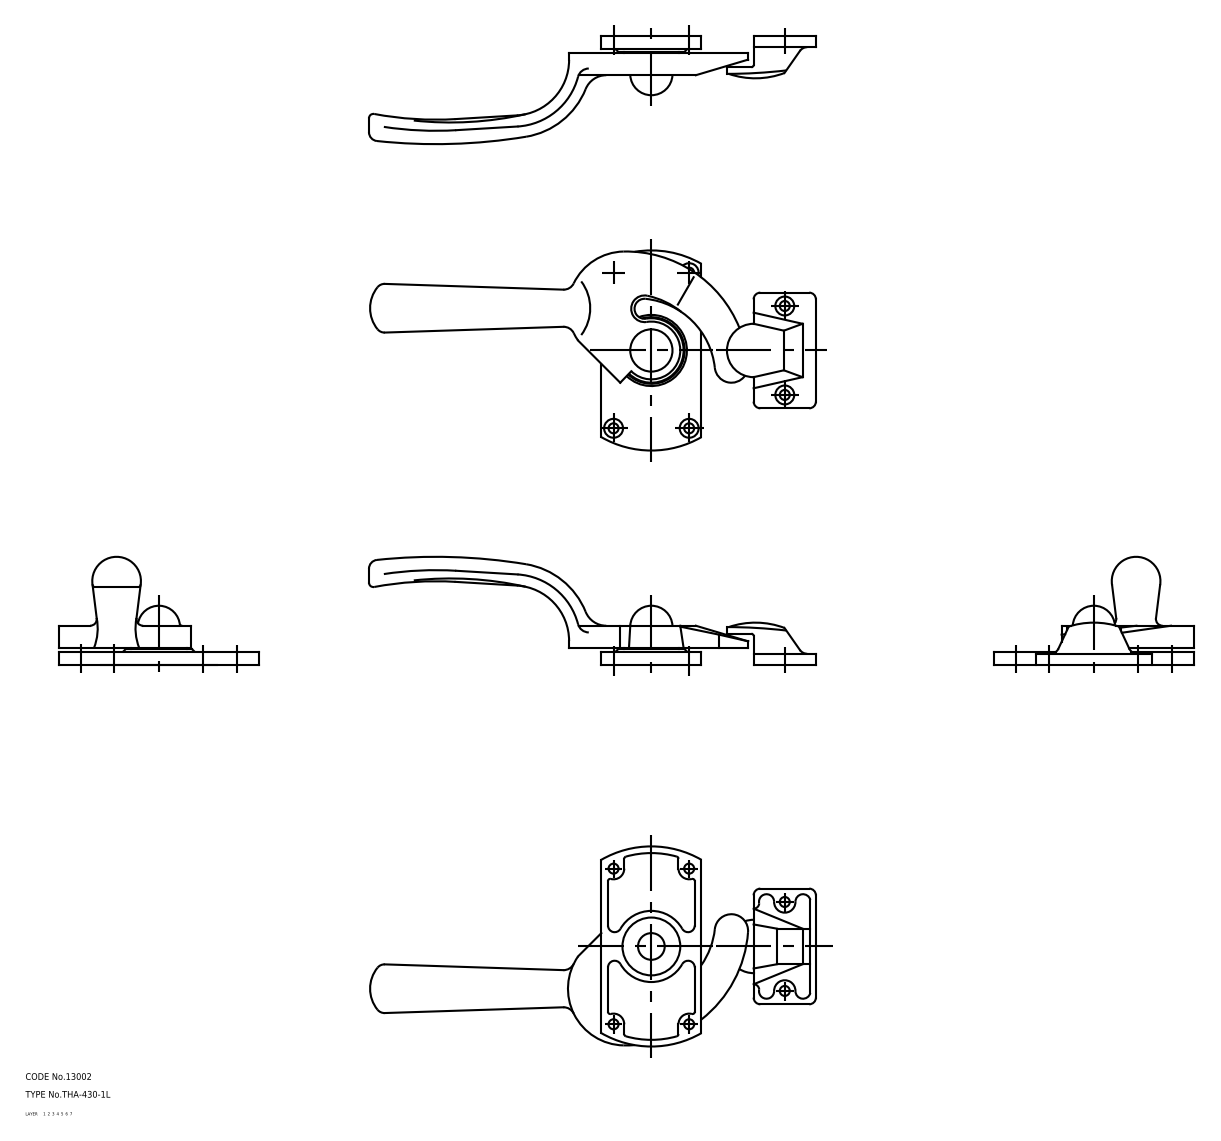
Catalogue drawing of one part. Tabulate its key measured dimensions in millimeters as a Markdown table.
| quantity | value |
| --- | --- |
| part name | washer_C; washer_B; rivet; keeper (+3 more) |
| STEP written by | CADfix (AUTOMOTIVE_DESIGN) |
| units | millimeters |
| bodies | 6 solids, 174 faces (0 planar, 0 cylindrical, 174 other) |
| overall size | 201 × 90 × 48.59 |
| volume | 72 958 mm³ |
| surface area | 32 856 mm² |
